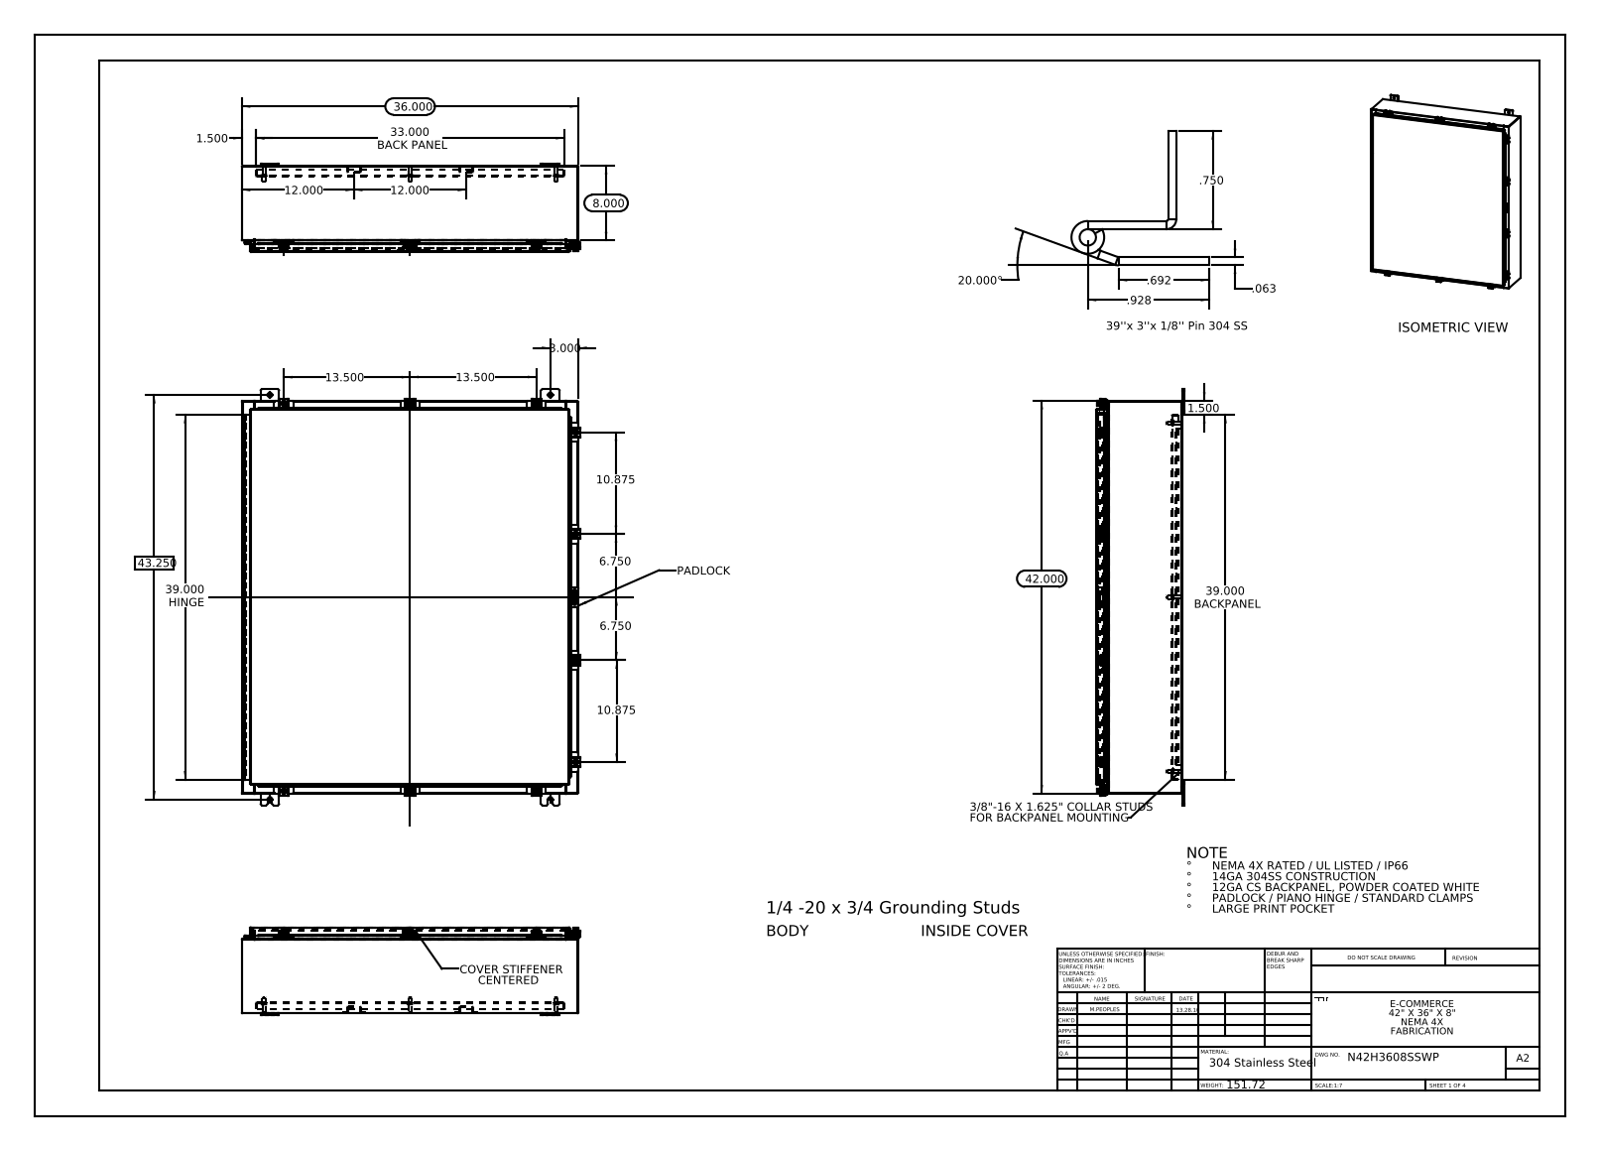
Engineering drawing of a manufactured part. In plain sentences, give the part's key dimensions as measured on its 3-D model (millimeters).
The part is named "N42H3608SSWP 125 Pin Hinge; N42H3608SSWP Mounting Feet; N42H3608SSWP Standard Clamps; N42H3608SSWP Door Stiffener (+8 more)". Its 3-D file was written by "SolidWorks 2013 (CONFIG_CONTROL_DESIGN)". It is 74 solids with 2855 faces: 1490 planar, 1197 cylindrical and 168 other. Overall it measures 1130.3 by 919.8 by 238.5 millimeters. Its volume is 8 718 000 cubic millimeters and its surface area 8 531 000 square millimeters. Round holes: 12 of diameter 12.7, 10 of diameter 5.4, 10 of diameter 6.6, 6 of diameter 6.4, 2 of diameter 3.2, 1 of diameter 3.2. Round bosses or shafts: 11 of diameter 6.4, 10 of diameter 12.7, 10 of diameter 10.1, 8 of diameter 15.9, 8 of diameter 9.5, 8 of diameter 8.4. Partial cylindrical surfaces (rounded edges, fillets, slot ends): 46 of radius 1.5, 39 of radius 0.3, 33 of radius 2.2, 24 of radius 4.8, 20 of radius 3, 20 of radius 3.6, 15 of radius 1.3, 14 of radius 2. The main face-to-face distances are 1.9, 231.8, 229.9, 233.7, 2.6, 25.4, 206.4, 27.3, 204.5, 29.9. The hole center spacings are 342.9, 347, 431.8, 435.5, 473.1, 529.2, 617.5, 659.3.
